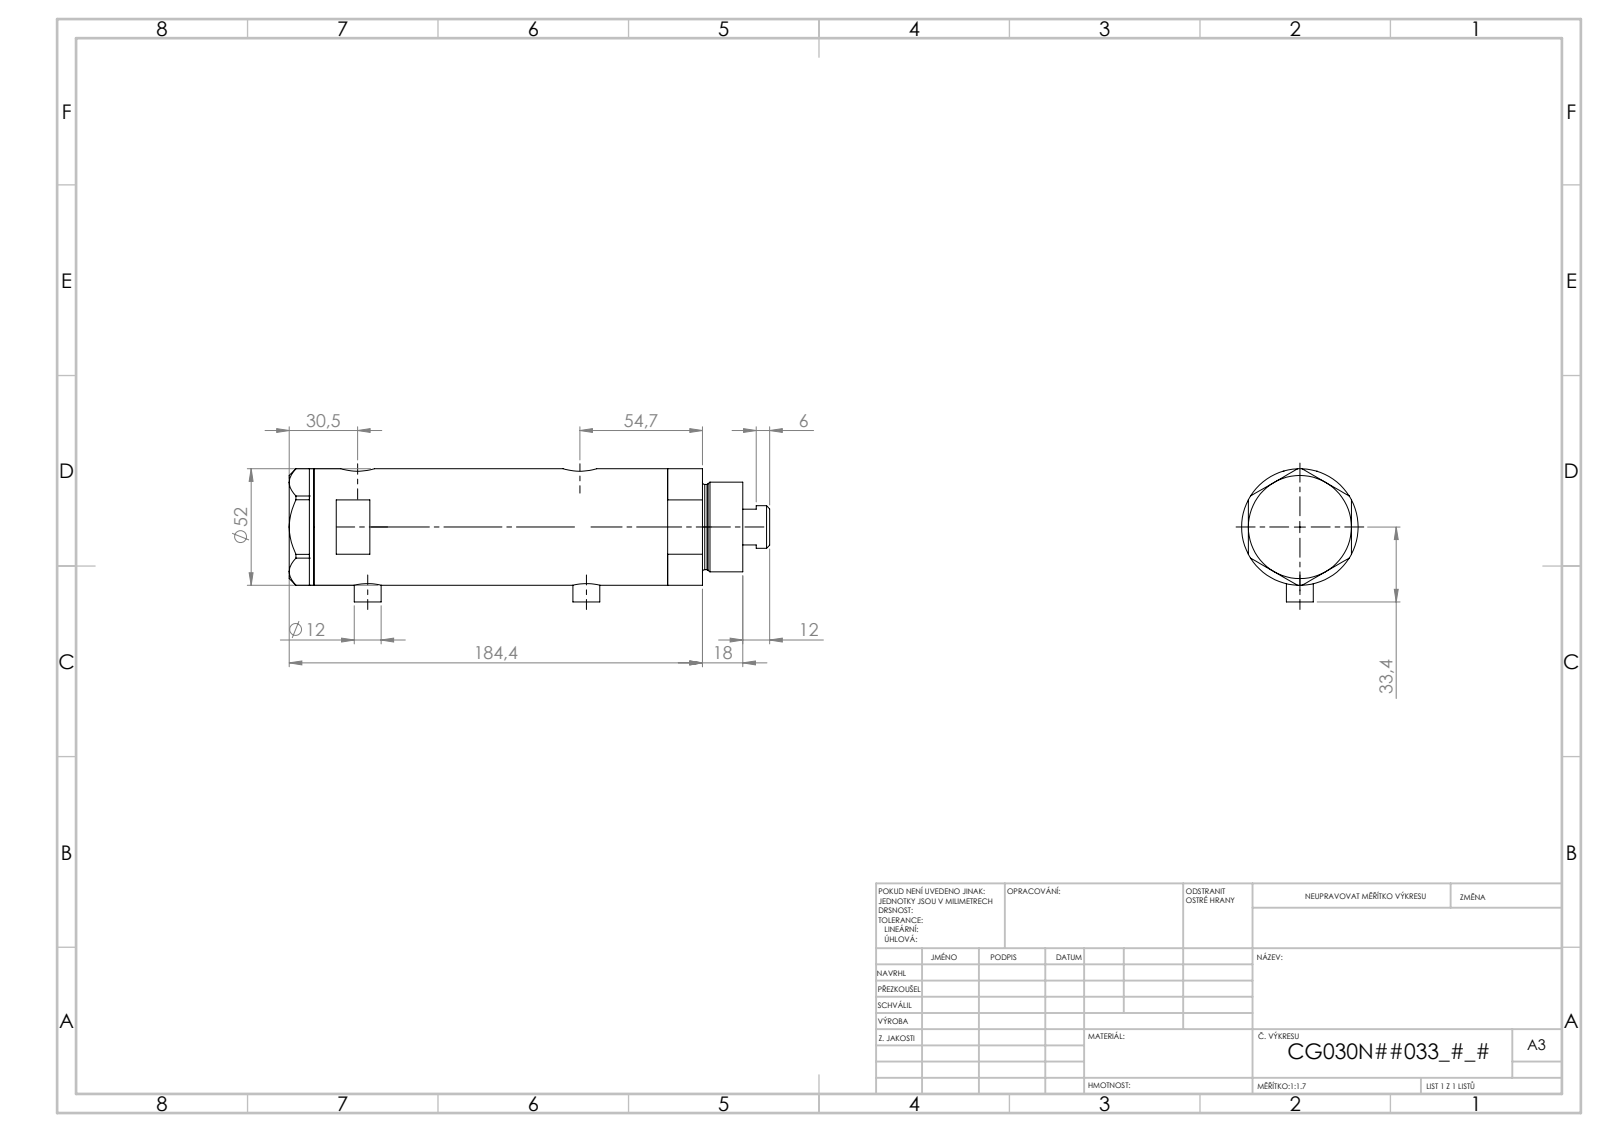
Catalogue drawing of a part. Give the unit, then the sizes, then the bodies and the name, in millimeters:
Units: millimetres
Overall size (bounding box): 214.4 × 59.4 × 52
Round holes (diameter × count): ⌀9.73 ×2, ⌀12.5 ×2, ⌀15 ×2, ⌀6.5 ×1, ⌀20 ×1, ⌀21.5 ×1, ⌀30 ×1, ⌀33 ×1, ⌀44 ×1
Round bosses / shafts (diameter × count): ⌀12 ×2, ⌀52 ×1, ⌀40 ×1, ⌀38 ×1, ⌀19 ×1
Main face-to-face distances: 121.5, 23.8, 97.7, 11, 34.8, 132.5, 46, 168.9, 157.9, 134.1
Hole centre spacings: 2.9, 4.5, 94.7, 97.6, 99.2, 102.1
Volume: 397 453 mm³ · Surface area: 87 596 mm²
Bodies: 4 solids, 134 faces (65 planar, 49 cylindrical, 20 other)
Part name (STEP PRODUCT): V270CG_VC; V270CG_FRONT; V270CG_BACK; V270CG_MIDDLE
STEP written by: SolidWorks 2019 (CONFIG_CONTROL_DESIGN)
